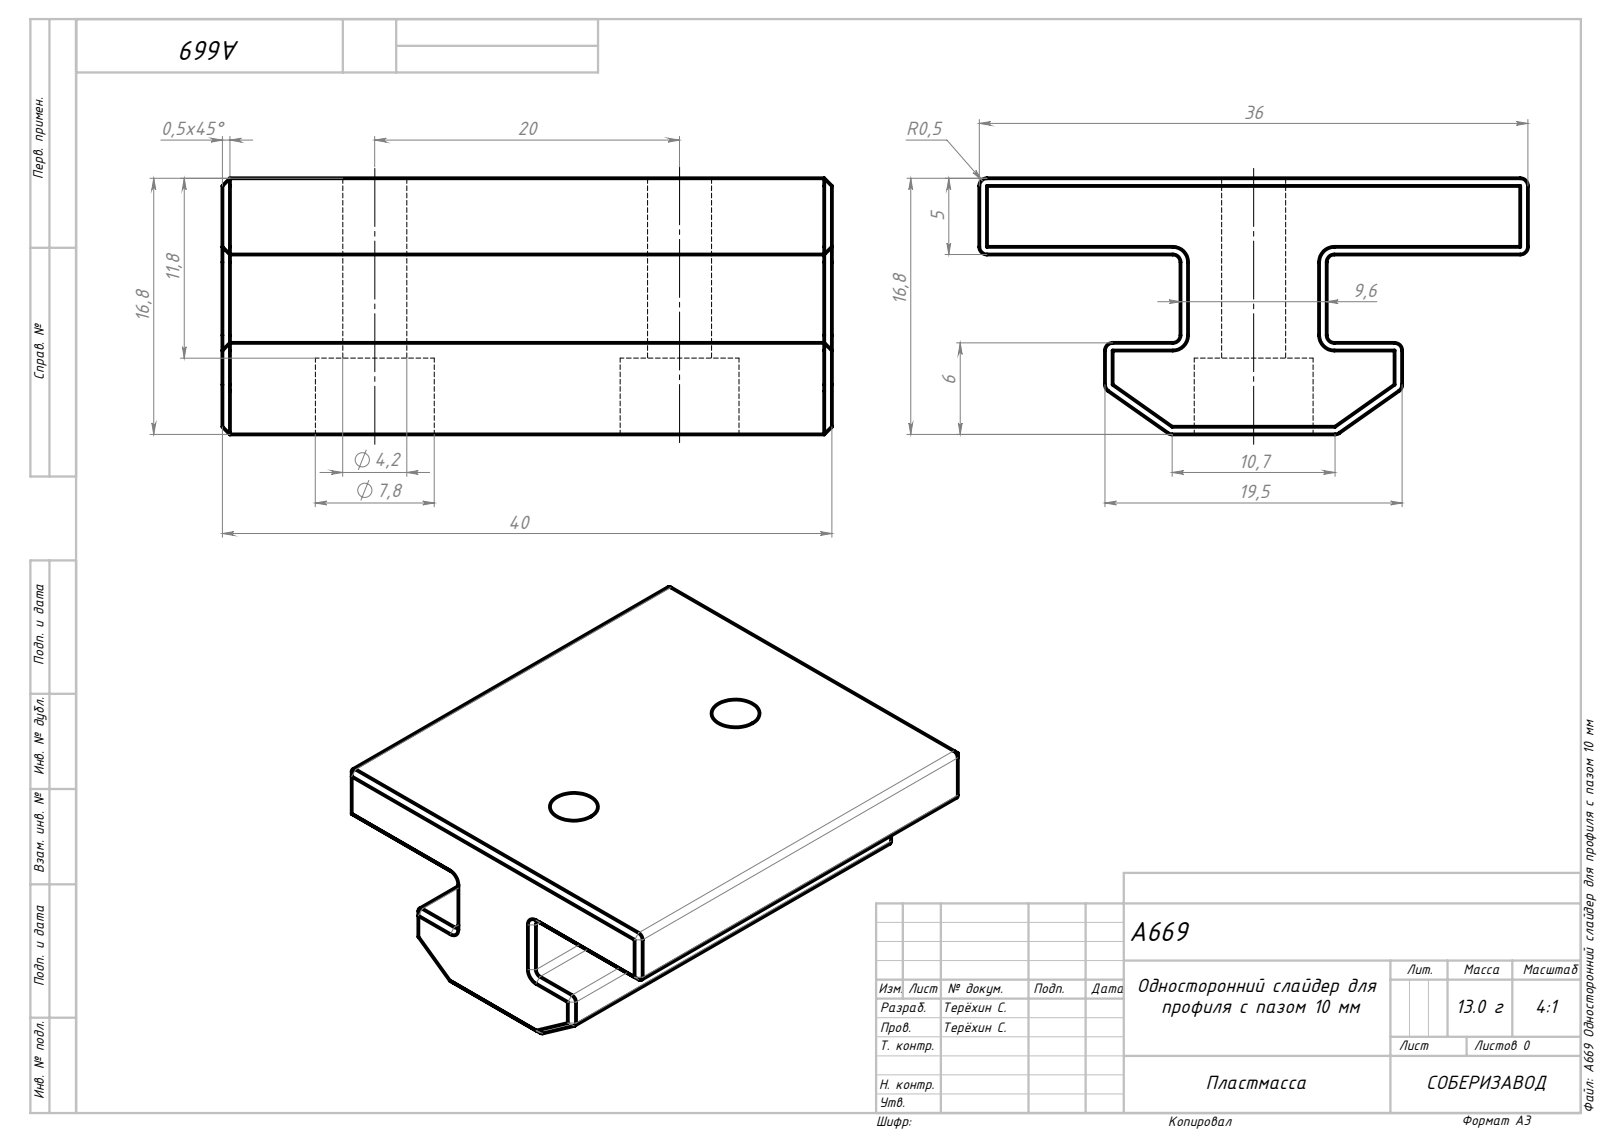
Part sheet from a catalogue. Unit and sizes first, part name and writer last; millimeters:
Units: millimetres
Overall size (bounding box): 40 × 36 × 16.8
Round holes (diameter × count): ⌀4.2 ×2, ⌀7.8 ×2
Partial cylindrical surfaces — rounded edges, fillets, slot ends (radius × count): R0.5 ×14
Main face-to-face distances: 5, 11.8, 16.8, 13.2, 22.8, 6, 5.8, 10.8, 40, 9.6
Hole centre spacings: 20
Volume: 12 758 mm³ · Surface area: 5 873 mm²
Bodies: 1 solid, 96 faces (46 planar, 22 cylindrical, 28 other)
Part name (STEP PRODUCT): Односторонний слайдер 10 паз
STEP written by: SolidWorks 2021 (AUTOMOTIVE_DESIGN)
